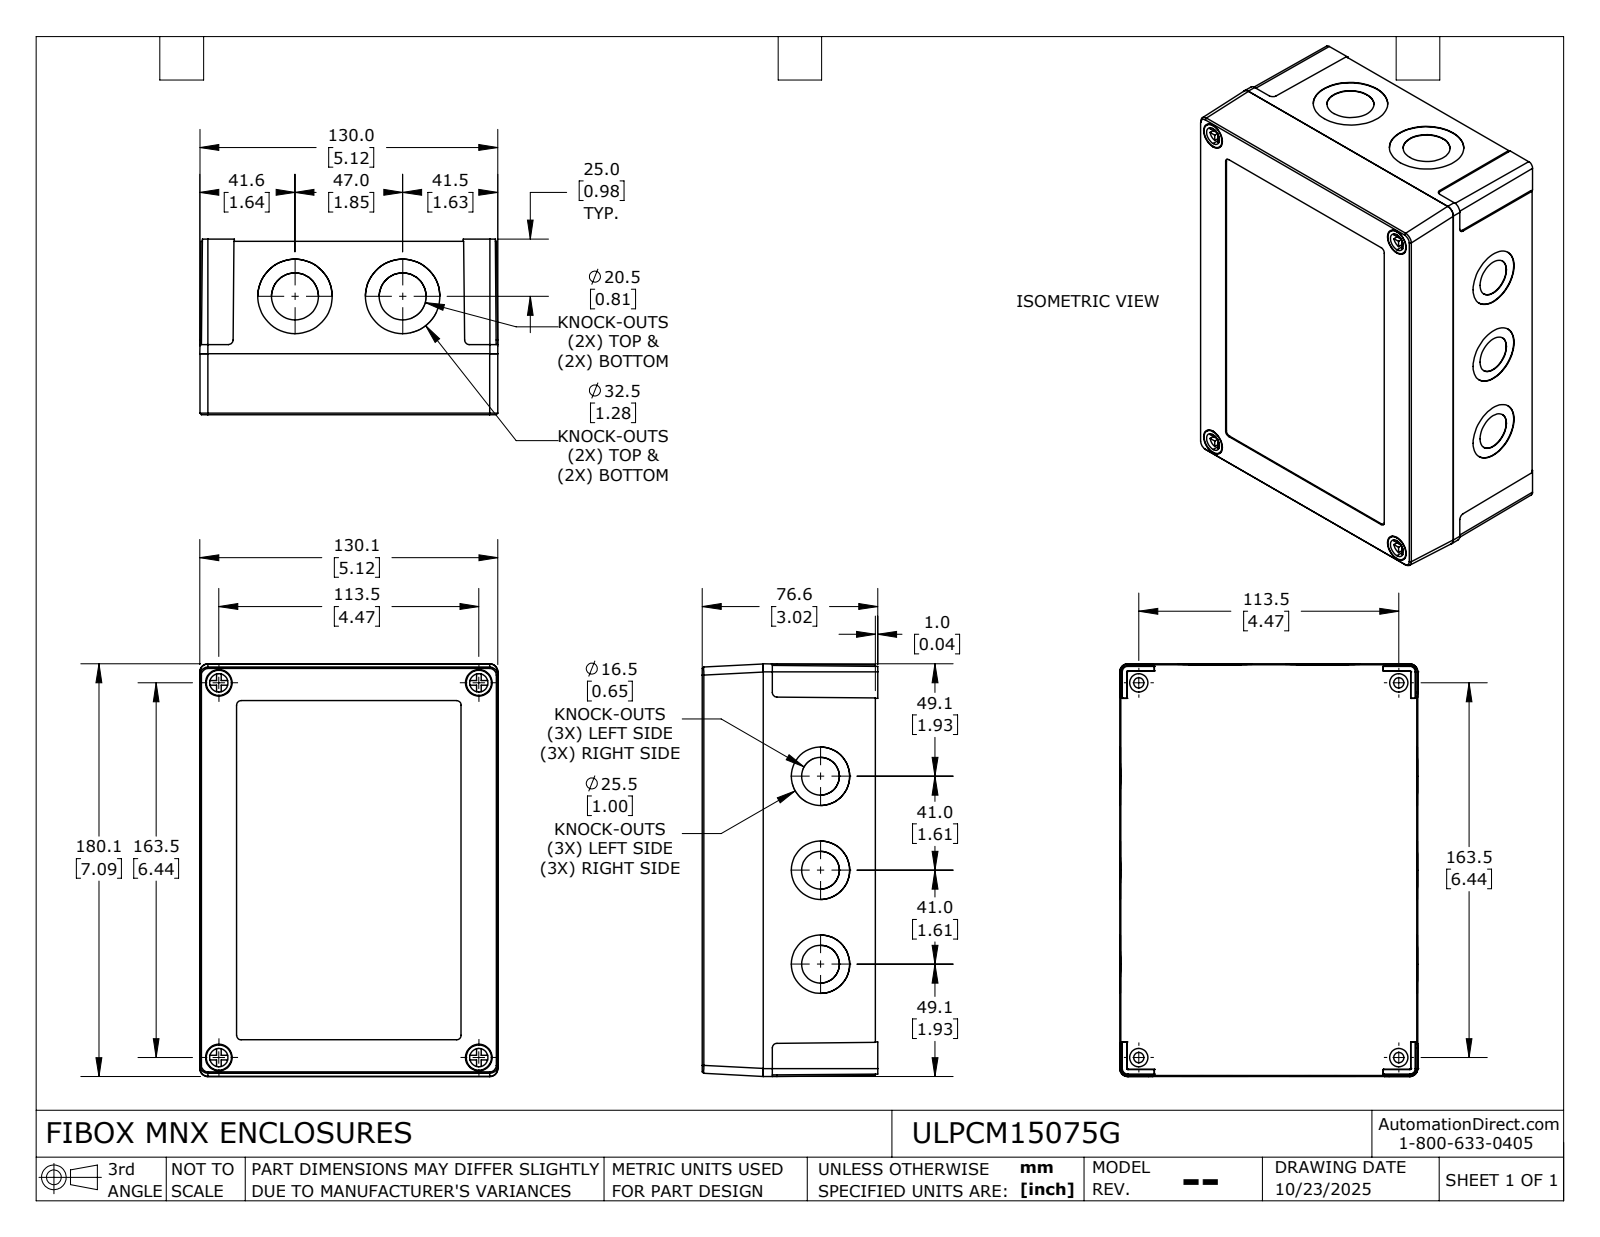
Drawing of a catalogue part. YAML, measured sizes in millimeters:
part_name: "ULPCM15075G_Default"
step_written_by: "SolidWorks 2024 (CONFIG_CONTROL_DESIGN)"
units: millimeters
bodies: {solids: 6, faces: 534, planar: 302, cylindrical: 196, other: 36}
overall_size: [180.1, 130.1, 76.6]
volume: 315900
surface_area: 195400
round_holes:
  - {diameter: 3.2, count: 8}
  - {diameter: 4, count: 8}
  - {diameter: 16.5, count: 6}
  - {diameter: 25.5, count: 6}
  - {diameter: 4.5, count: 4}
  - {diameter: 8, count: 4}
  - {diameter: 11.6, count: 4}
  - {diameter: 20.5, count: 4}
  - {diameter: 32.5, count: 4}
round_bosses_or_shafts:
  - {diameter: 8, count: 8}
  - {diameter: 2.5, count: 8}
  - {diameter: 11, count: 4}
  - {diameter: 7.2, count: 4}
partial_cylinders:
  - {radius: 2, count: 8}
  - {radius: 1.4, count: 6}
  - {radius: 0.5, count: 4}
  - {radius: 3.5, count: 4}
  - {radius: 5, count: 4}
  - {radius: 0.6, count: 2}
face_to_face_distances: [73.1, 3, 70.1, 4.2, 2, 72.1, 75.1, 72.6, 2.5, 0.5]
hole_center_spacings: [33.9, 41, 49.3, 50, 57.9, 82.6, 83.2, 103]
